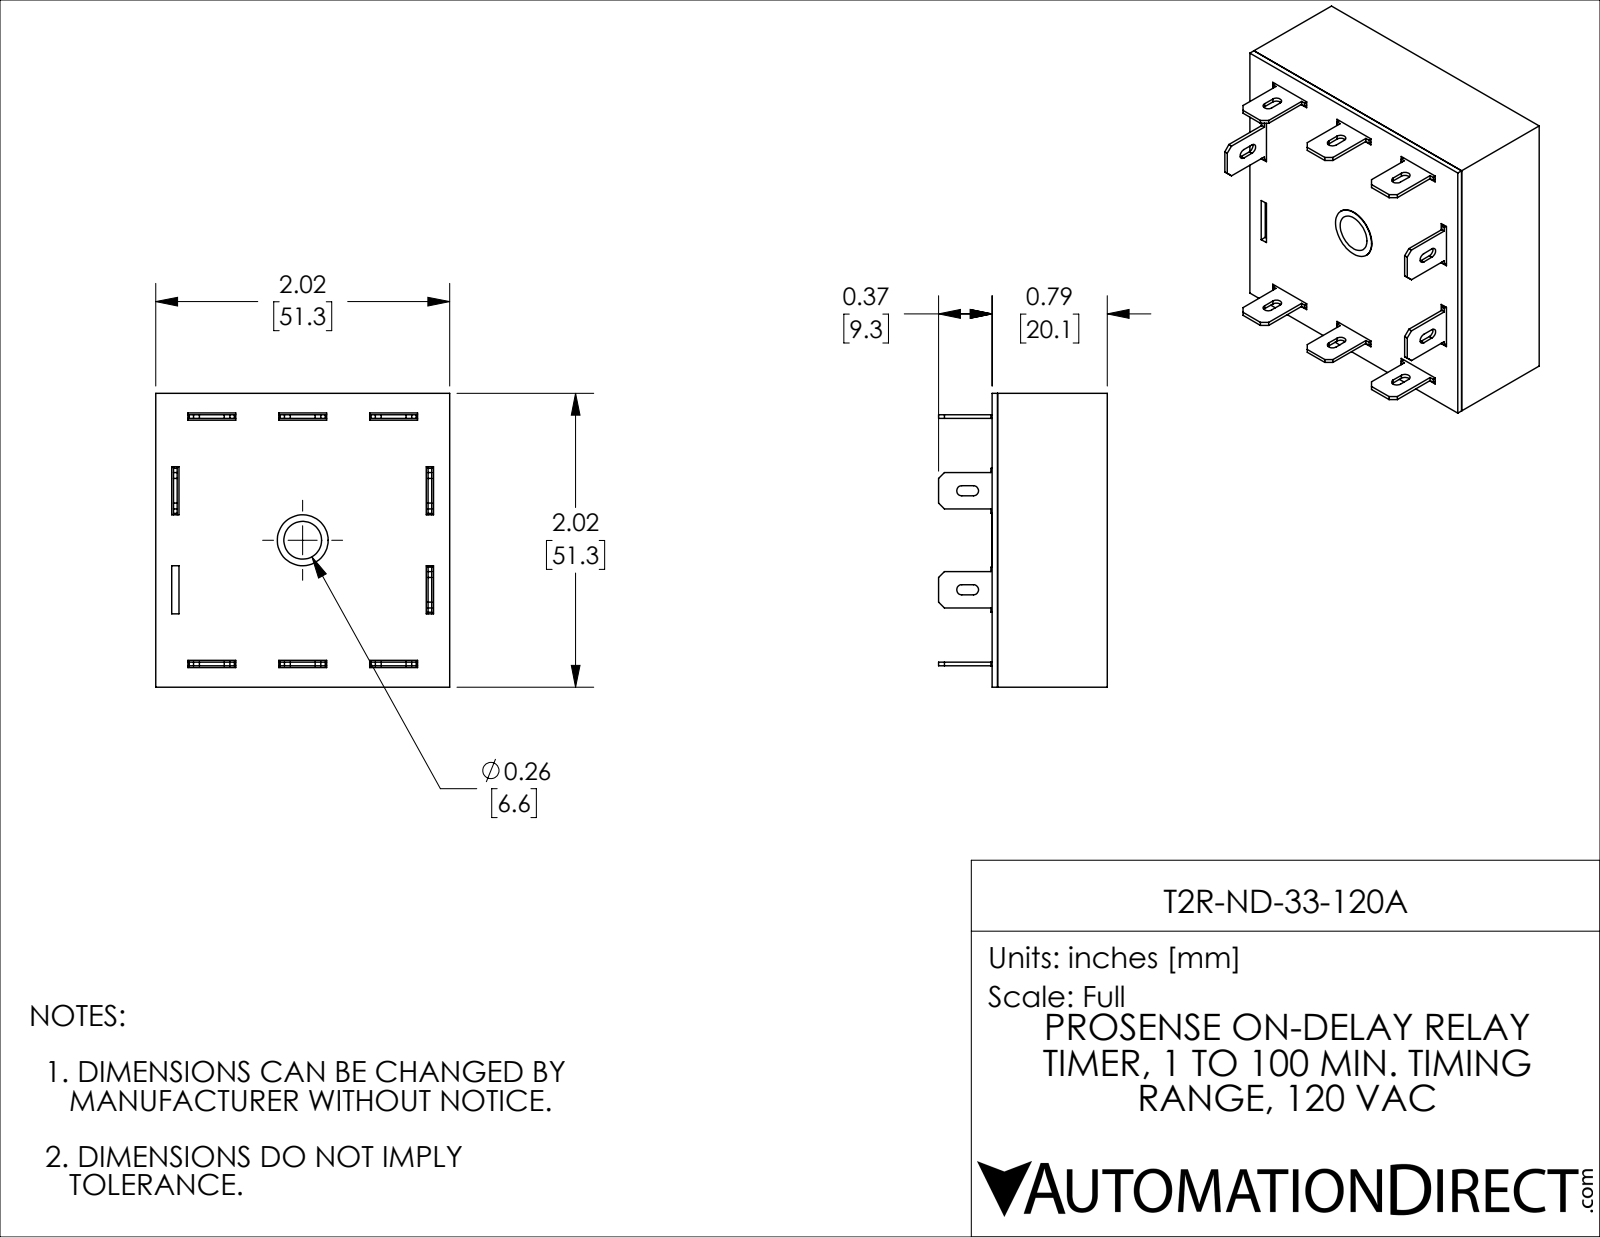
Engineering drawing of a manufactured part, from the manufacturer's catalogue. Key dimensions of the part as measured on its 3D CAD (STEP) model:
Part name (STEP PRODUCT): T2R-ND-33-120A
STEP written by: SolidWorks 2021 (CONFIG_CONTROL_DESIGN)
Units: millimetres
Bodies: 11 solids, 280 faces (256 planar, 22 cylindrical, 2 other)
Overall size (bounding box): 51.31 × 51.31 × 29.46
Volume: 11 178 mm³ · Surface area: 23 301 mm²
Round holes (diameter × count): ⌀8.89 ×1
Partial cylindrical surfaces — rounded edges, fillets, slot ends (radius × count): R0.89 ×10
Main face-to-face distances: 1.14, 50.16, 19.15, 20.12, 0.97, 18.01, 18.98, 51.3, 3.74, 47.56
